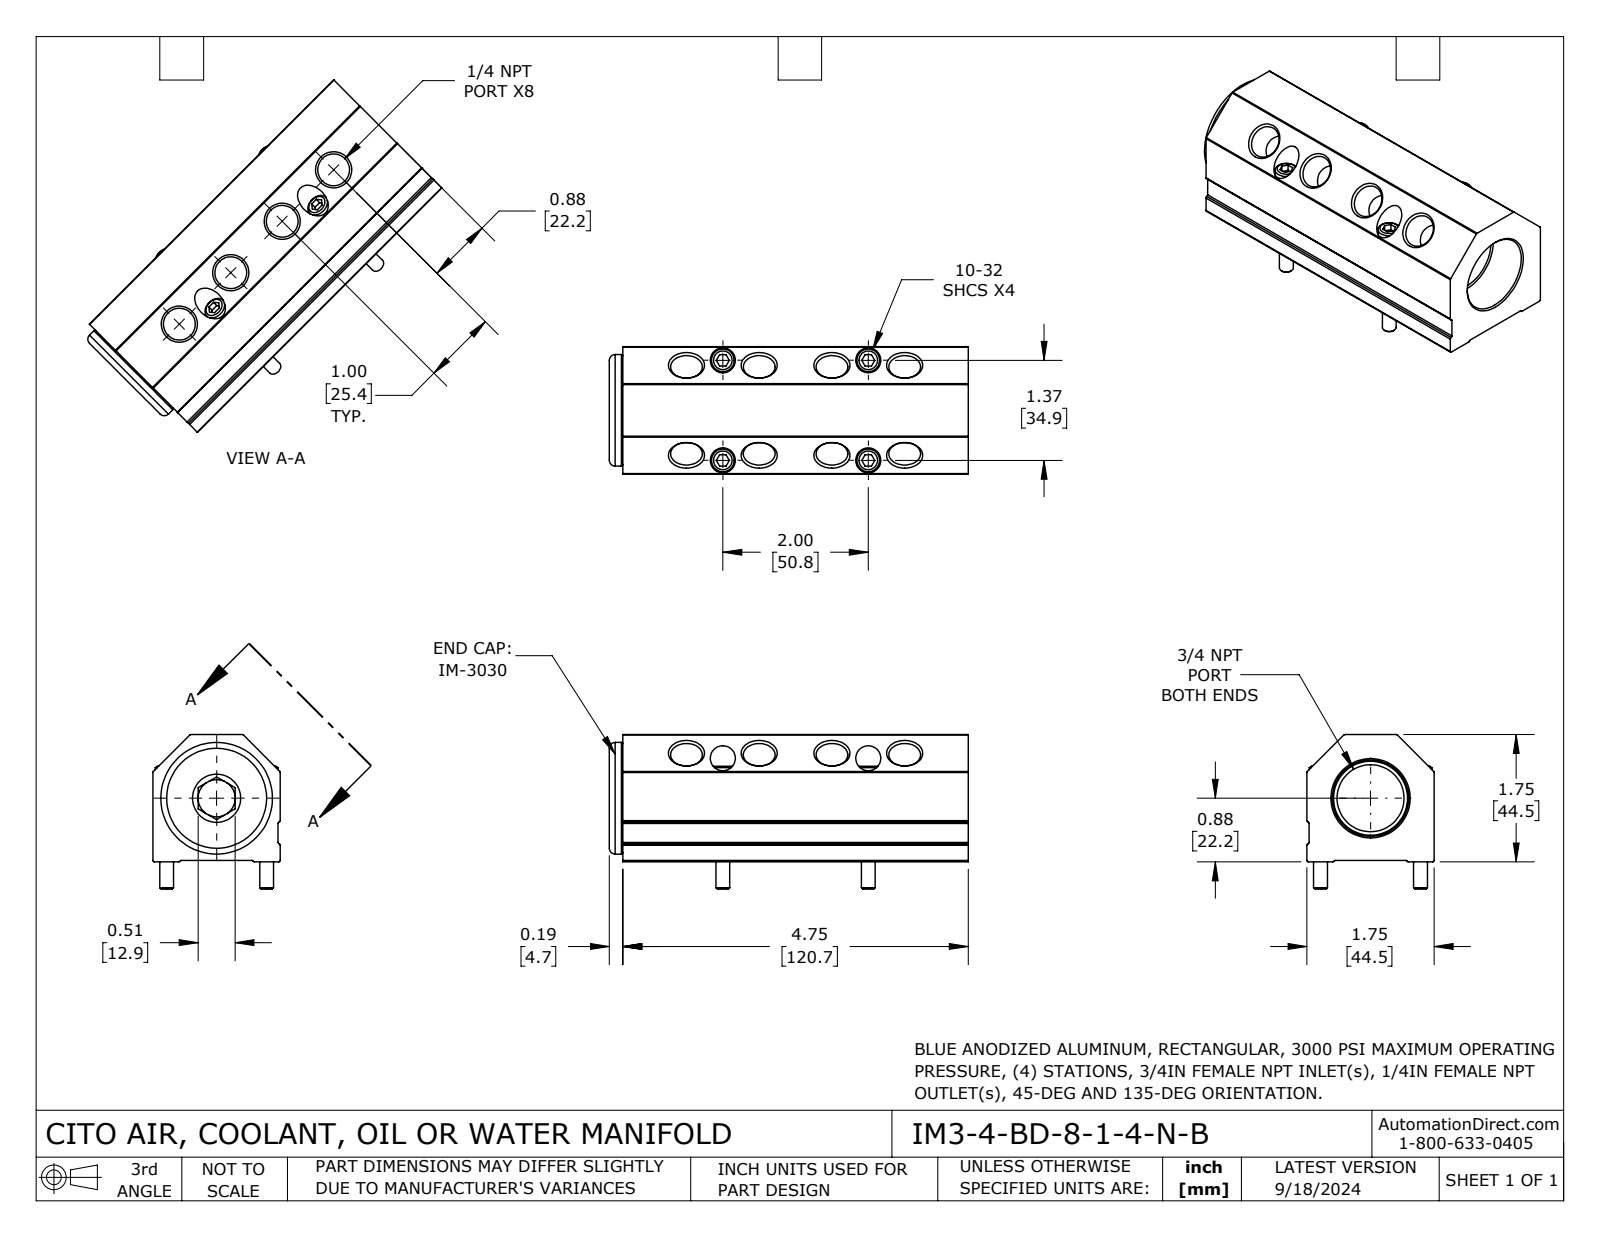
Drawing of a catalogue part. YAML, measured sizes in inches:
part_name: "IM3-4-BD-8-1-4-N-B"
step_written_by: "SolidWorks 2023 (CONFIG_CONTROL_DESIGN)"
units: inches
bodies: {solids: 6, faces: 216, planar: 82, cylindrical: 74, other: 60}
overall_size: [4.935, 2.125, 1.75]
volume: 9.729
surface_area: 66.59
round_holes:
  - {diameter: 0.437, count: 8}
  - {diameter: 0.203, count: 4}
  - {diameter: 0.344, count: 4}
  - {diameter: 0.51, count: 1}
  - {diameter: 0.921, count: 1}
  - {diameter: 1.394, count: 1}
round_bosses_or_shafts:
  - {diameter: 0.312, count: 4}
  - {diameter: 0.19, count: 4}
  - {diameter: 1.534, count: 1}
  - {diameter: 1.182, count: 1}
  - {diameter: 0.938, count: 1}
partial_cylinders:
  - {radius: 0.02, count: 14}
face_to_face_distances: [1.75, 1.73, 0.02, 1.75, 4.75, 0.03, 1.72, 0.185, 4.935, 0.531]
hole_center_spacings: [1, 2, 1.375, 2.427, 3]
